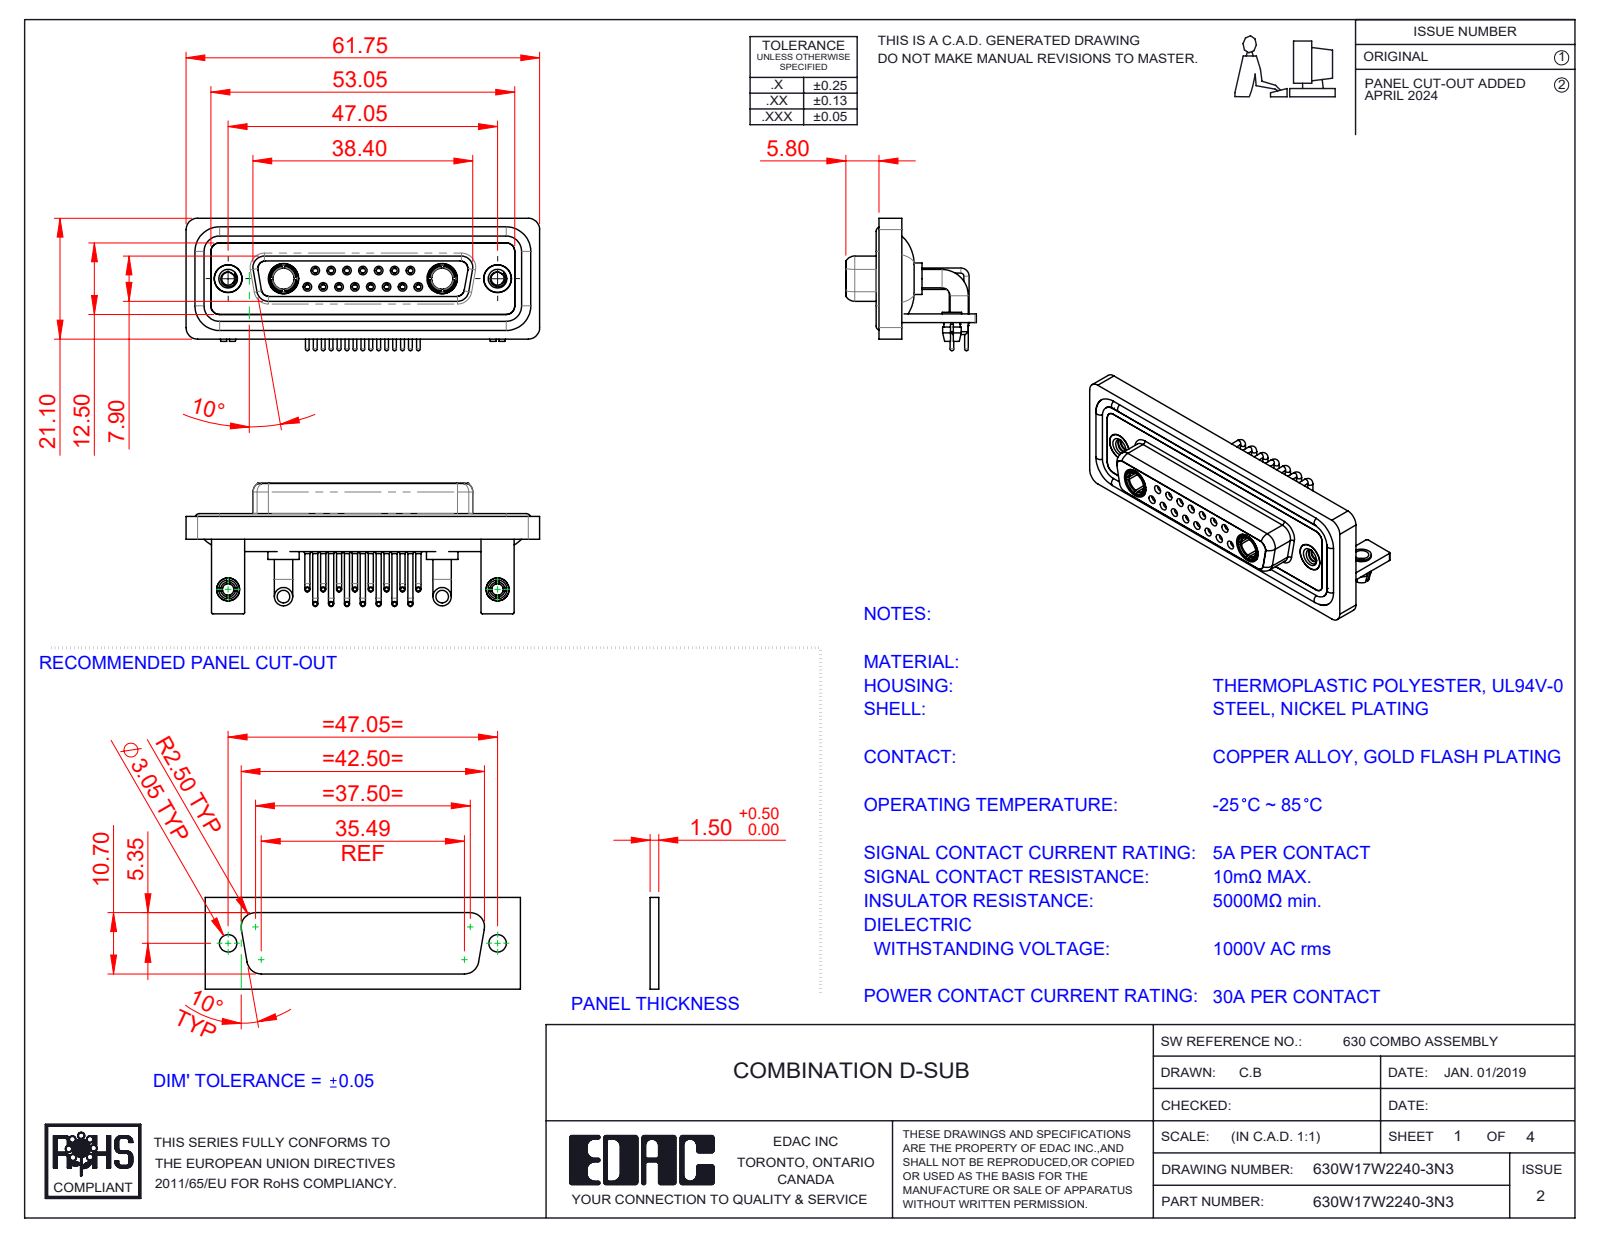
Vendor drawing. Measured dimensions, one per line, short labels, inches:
name: 630Combo Contact Row 1_50 Contacts; 630Combo Contact Row 2_50 Contacts; 630Combo Threaded Rivet_2; 630Combo Board Lock_50 Contacts (+7 more)
written by: SolidWorks 2023 (CONFIG_CONTROL_DESIGN)
unit: in
bodies: 30 solids, 1477 faces (456 planar, 639 cylindrical, 382 other)
size: 2.431 × 0.91 × 0.898
volume: 0.546 in³; area: 24.05 in²
holes: 17× ⌀0.079, 15× ⌀0.035, 15× ⌀0.043, 15× ⌀0.059, 8× ⌀0.063, 7× ⌀0.067, 4× ⌀0.191, 2× ⌀0.089, 2× ⌀0.098, 2× ⌀0.126, 2× ⌀0.146, 2× ⌀0.157
bosses: 15× ⌀0.035, 15× ⌀0.026, 11× ⌀0.063, 4× ⌀0.126, 2× ⌀0.217, 2× ⌀0.205, 2× ⌀0.195, 2× ⌀0.195
rounds: 19× R0.079, 18× R0.059, 16× R0.01, 8× R0.053, 8× R0.063, 5× R0.02, 4× R0.024, 4× R0.026
face distances: 0.016, 0.071, 0.114, 0.146, 0.059, 0.161, 0.043, 0.055, 0.063, 0.122
hole spacings: 0.124, 0.109, 0.218, 0.327, 0.198, 0.295, 0.436, 0.198
